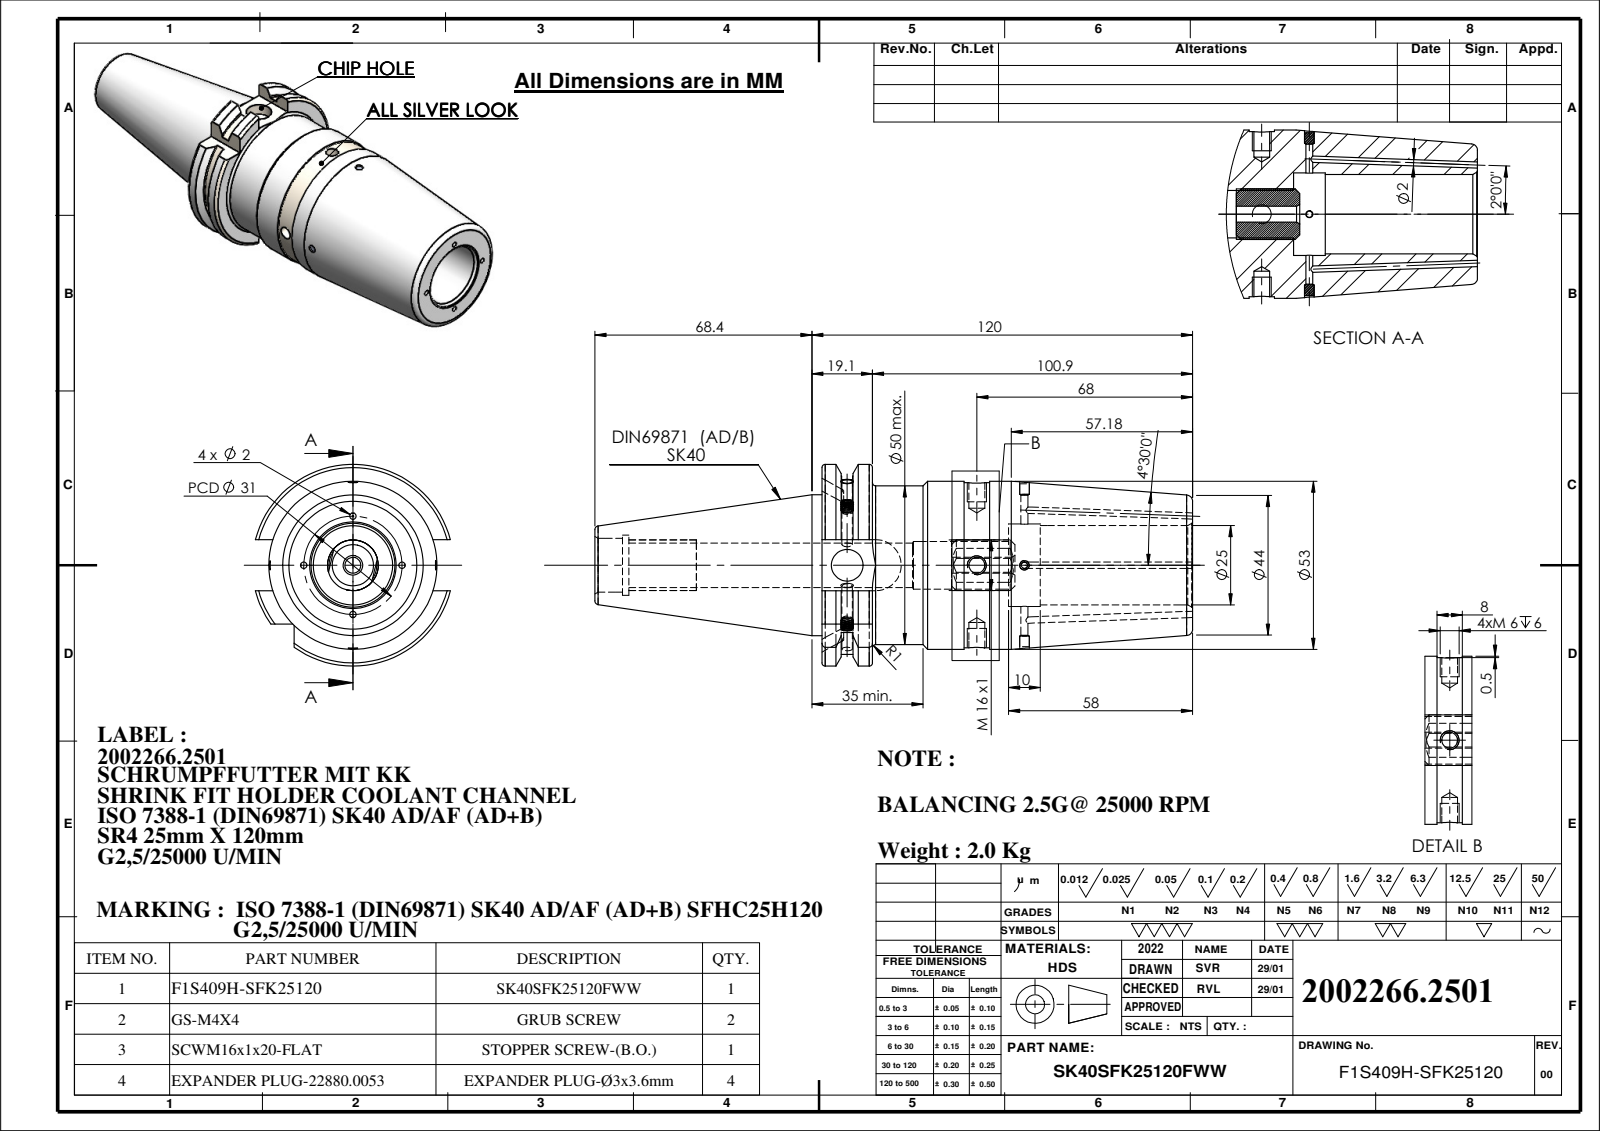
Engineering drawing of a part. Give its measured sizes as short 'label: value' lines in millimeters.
name: GS-M4X4_DIN 913 - M4 x 4-N; EXPANDER PLUG Ø3x3.6; SK40SFK25120FWW; 91406-SR425120 (+1 more)
written by: SolidWorks 2018 (CONFIG_CONTROL_DESIGN)
unit: mm
bodies: 8 solids, 296 faces (63 planar, 107 cylindrical, 126 other)
size: 188.4 × 63.55 × 61.48
volume: 261 454 mm³; area: 47 520 mm²
holes: 4× ⌀2, 3× ⌀5, 2× ⌀2.2, 2× ⌀3, 1× ⌀3.3, 1× ⌀10, 1× ⌀14, 1× ⌀15, 1× ⌀17, 1× ⌀19, 1× ⌀24.99, 1× ⌀25.99
bosses: 2× ⌀4, 1× ⌀53, 1× ⌀52, 1× ⌀50, 1× ⌀44.45
rounds: 1× R8, 1× R8.05, 1× R28.12, 1× R31.77
face distances: 116.8, 15.9, 100.9, 58.8, 42.9, 58, 14, 8, 47.8, 16.1
hole spacings: 15, 40.85, 55.85
